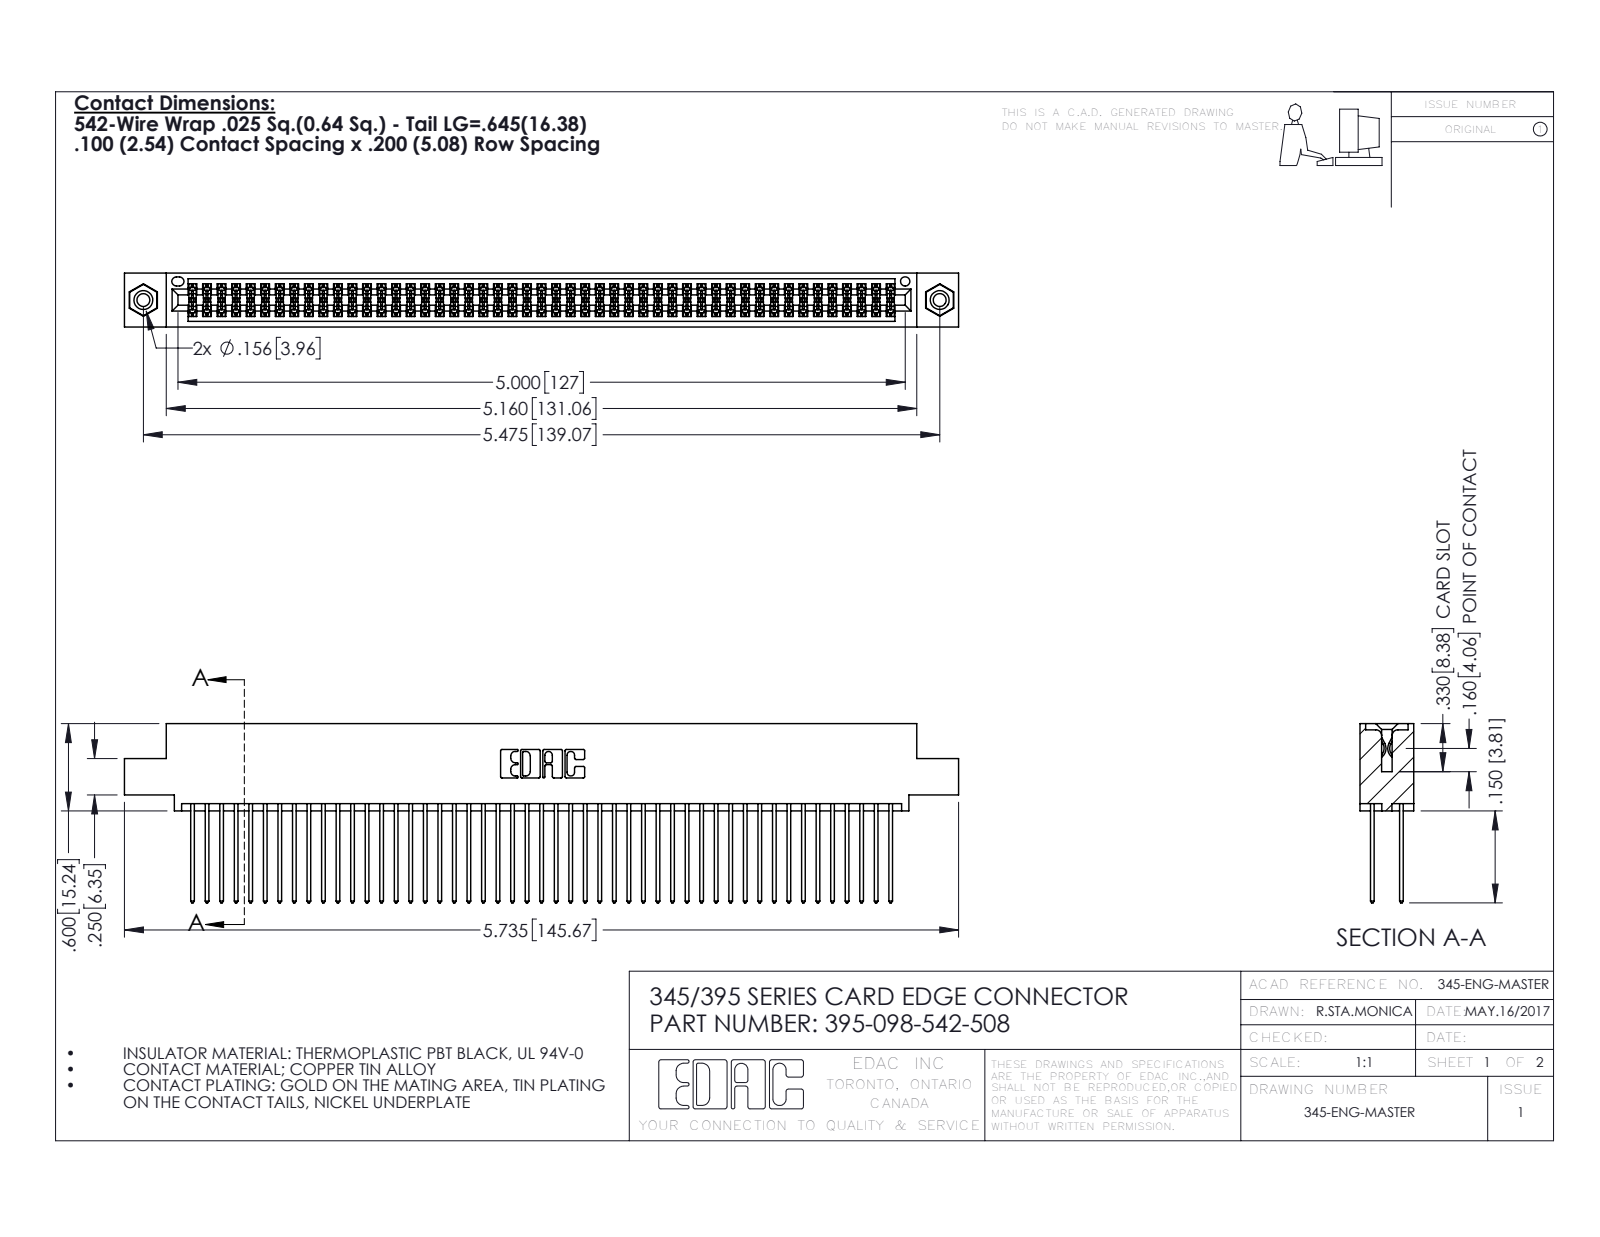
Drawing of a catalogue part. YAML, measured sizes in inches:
part_name: "395-098-542-508; 345-250-001_345-250-003-102; 345 Part_0.110 Offset - 0.156 Dia-TI; 345-292-001_345-293-142"
step_written_by: "SolidWorks 2016 (CONFIG_CONTROL_DESIGN)"
units: inches
bodies: {solids: 101, faces: 5090, planar: 3350, cylindrical: 1724, other: 16}
overall_size: [5.735, 1.232, 0.37]
volume: 0.89
surface_area: 37.12
round_holes:
  - {diameter: 0.089, count: 2}
  - {diameter: 0.125, count: 2}
  - {diameter: 0.156, count: 2}
  - {diameter: 0.064, count: 1}
round_bosses_or_shafts:
  - {diameter: 0.155, count: 2}
partial_cylinders:
  - {radius: 0.006, count: 147}
  - {radius: 0.01, count: 98}
  - {radius: 0.01, count: 22}
  - {radius: 0.007, count: 6}
  - {radius: 0.031, count: 6}
  - {radius: 0.026, count: 3}
  - {radius: 0.014, count: 2}
  - {radius: 0.019, count: 2}
face_to_face_distances: [0.072, 0.298, 0.2, 0.098, 0.272, 0.025, 0.225, 0.37, 0.175, 0.149]
hole_center_spacings: [0.27, 5.239, 5.475]
